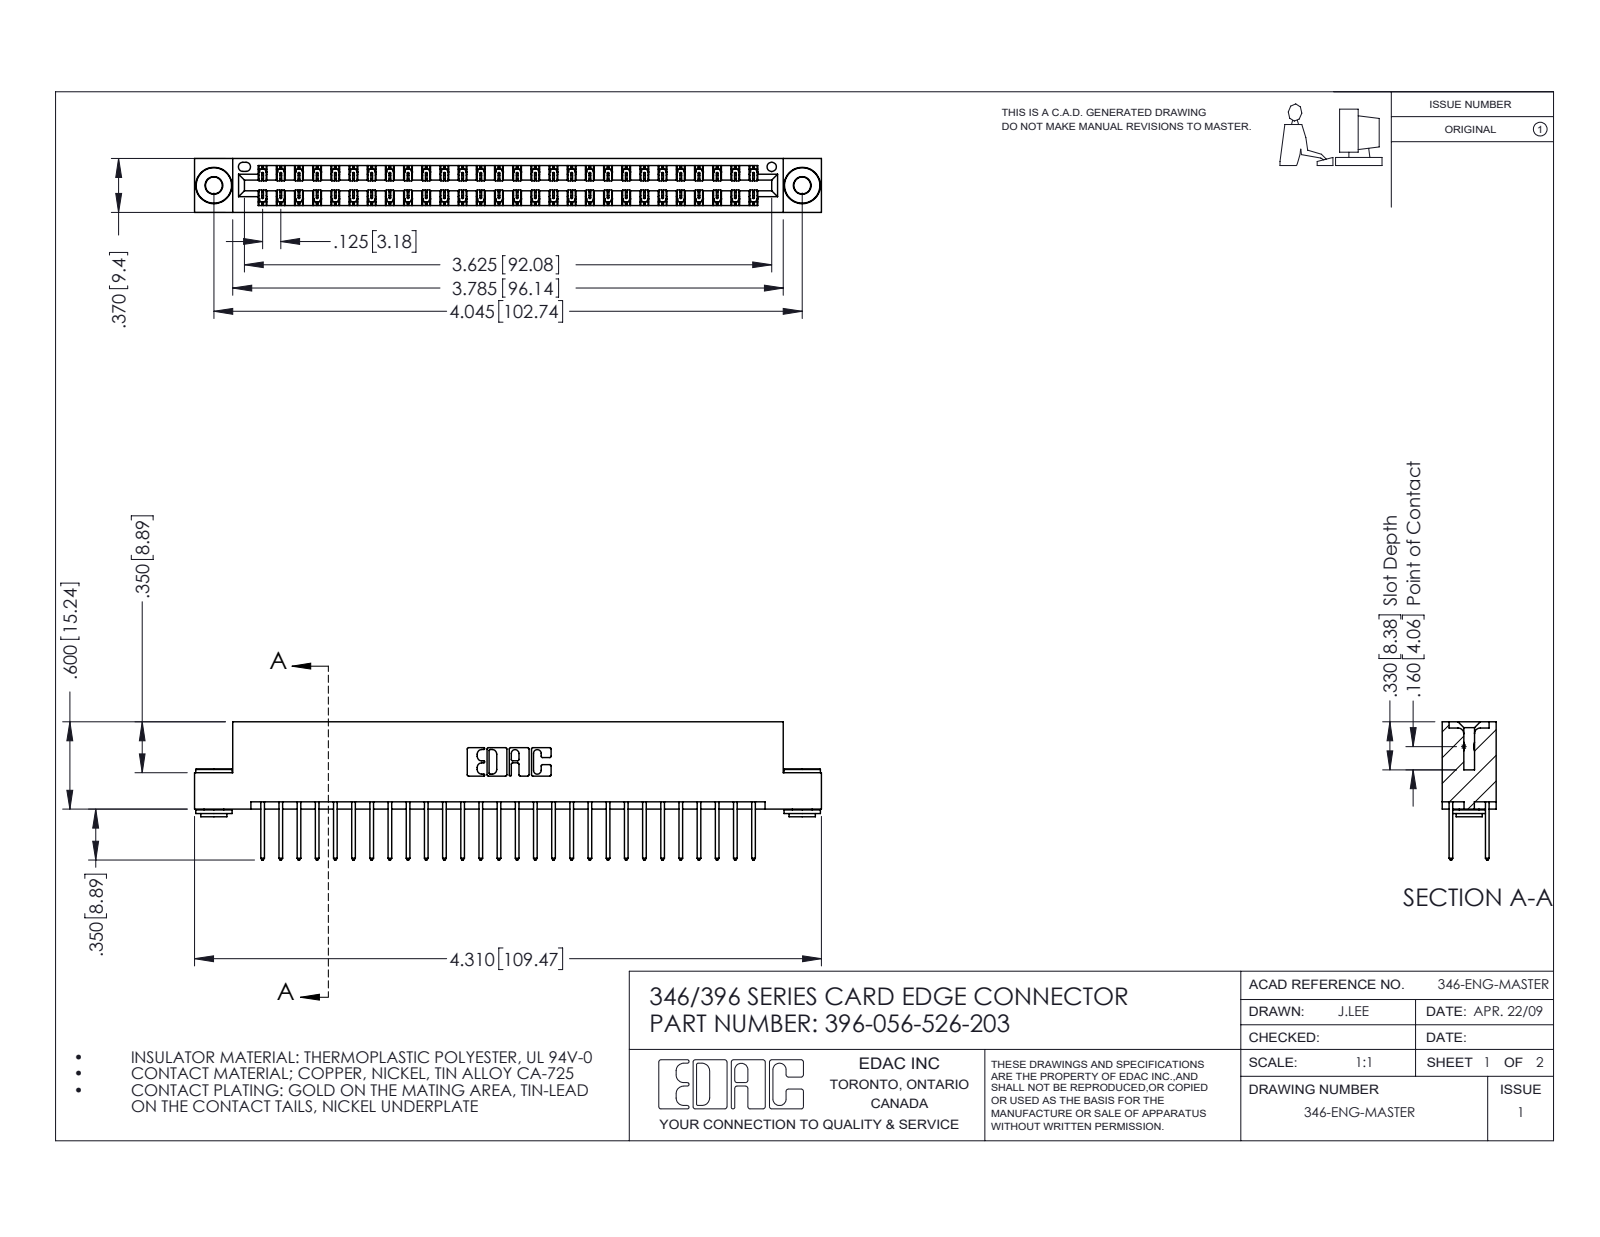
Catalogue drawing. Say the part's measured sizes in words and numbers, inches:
The part is named "346 Part_Flush Mounting Lugs - 0.156 Dia-TH; 396-056-526-203; 345-292-001_345-293-126; 345-250-002_345-250-002-102". Its 3-D file was written by "SolidWorks 2016 (CONFIG_CONTROL_DESIGN)". It is 59 solids with 3072 faces: 2046 planar, 1018 cylindrical and 8 other. Overall it measures 4.31 by 0.95 by 0.37 inches. Its volume is 0.652 cubic inches and its surface area 23.38 square inches. Round holes: 2 of diameter 0.116, 2 of diameter 0.156, 1 of diameter 0.064. Round bosses or shafts: 2 of diameter 0.25, 2 of diameter 0.18, 2 of diameter 0.136. Partial cylindrical surfaces (rounded edges, fillets, slot ends): 84 of radius 0.006, 56 of radius 0.01, 22 of radius 0.01, 6 of radius 0.007, 6 of radius 0.031, 3 of radius 0.026, 2 of radius 0.014, 2 of radius 0.022. The main face-to-face distances are 0.048, 0.322, 0.25, 0.37, 0.025, 0.072, 0.298, 0.275, 0.148, 0.222. The hole center spacings are 0.246, 3.837, 4.045.
